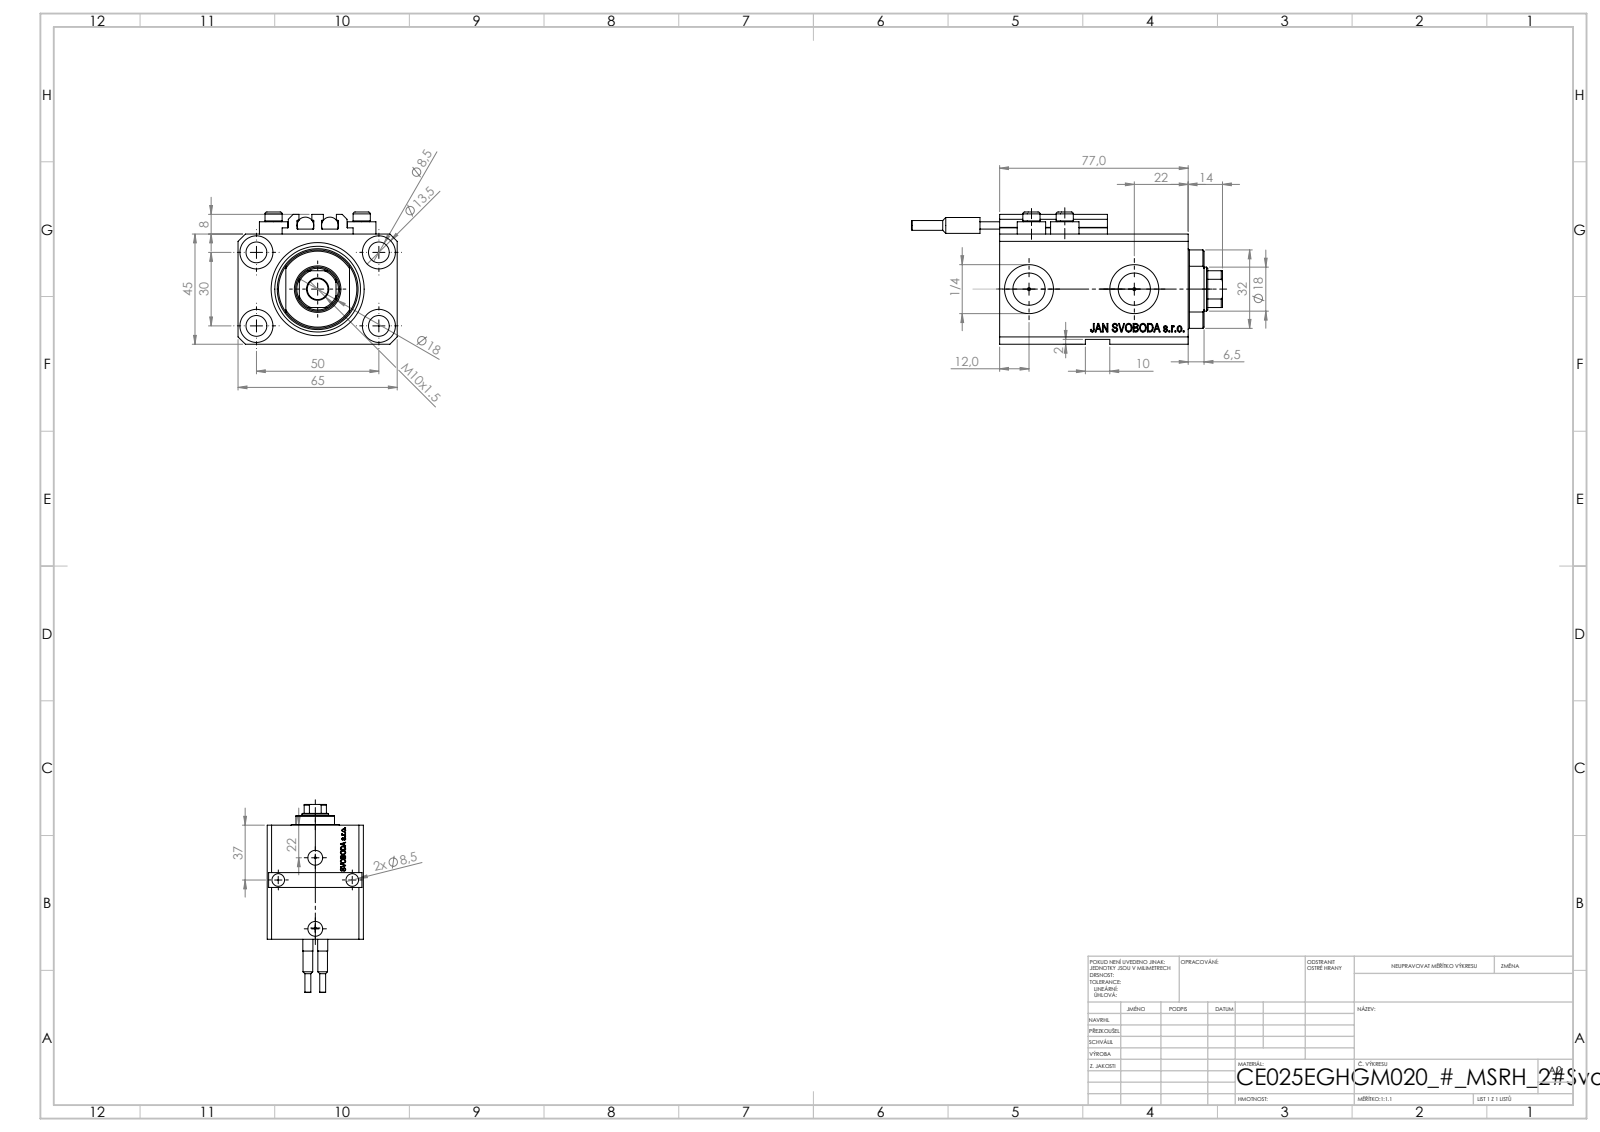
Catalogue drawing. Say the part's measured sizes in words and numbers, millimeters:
The part is named "V250CE_E_Body; V250CE_VC_E; SWITCH_V250CE; ALLEN BOLT V250CE (+1 more)". Its 3-D file was written by "SolidWorks 2019 (CONFIG_CONTROL_DESIGN)". It is 10 solids with 1119 faces: 543 planar, 138 cylindrical and 438 other. Overall it measures 127 by 65 by 54 millimeters. Its volume is 203 348 cubic millimeters and its surface area 61 935 square millimeters. Round holes: 7 of diameter 8.5, 4 of diameter 1.25, 4 of diameter 4, 4 of diameter 13.5, 2 of diameter 10, 2 of diameter 13.16, 2 of diameter 20, 1 of diameter 18, 1 of diameter 25, 1 of diameter 38. Round bosses or shafts: 4 of diameter 11.6, 4 of diameter 7, 2 of diameter 6.8, 2 of diameter 6.5, 2 of diameter 4. Partial cylindrical surfaces (rounded edges, fillets, slot ends): 10 of radius 0.2, 1 of radius 8.5, 1 of radius 16. The main face-to-face distances are 45, 65, 63, 2, 14, 3, 77, 47, 5, 6.9. The hole center spacings are 29.15, 50, 13.6, 15.12, 18.81, 18.97, 26.22, 26.61.
